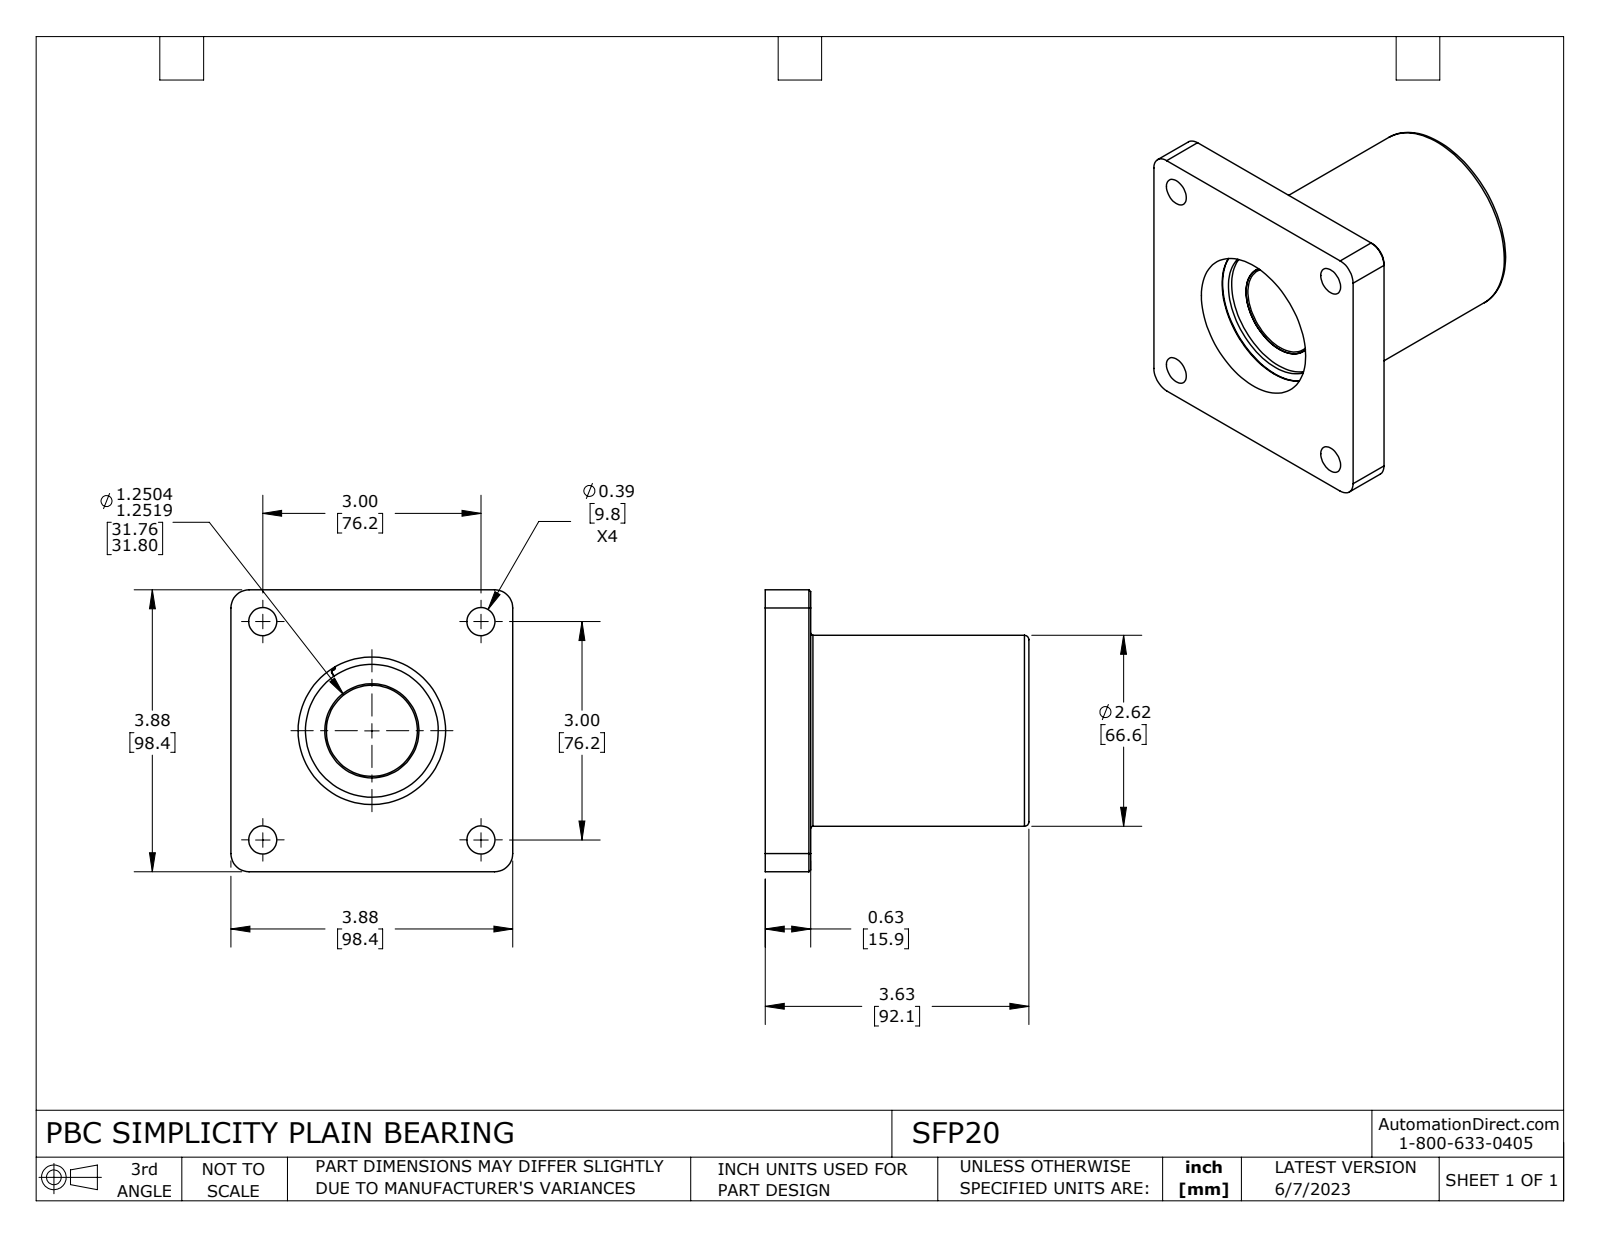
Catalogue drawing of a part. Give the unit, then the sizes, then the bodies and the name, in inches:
Units: inches
Overall size (bounding box): 3.875 × 3.875 × 3.625
Round holes (diameter × count): ⌀0.386 ×4, ⌀1.252 ×1, ⌀1.295 ×1, ⌀1.826 ×1, ⌀2.028 ×1, ⌀2.122 ×1
Round bosses / shafts (diameter × count): ⌀2.624 ×1, ⌀2.142 ×1, ⌀1.999 ×1, ⌀1.889 ×1, ⌀1.838 ×1
Partial cylindrical surfaces — rounded edges, fillets, slot ends (radius × count): R0.026 ×4, R0.25 ×4, R0.021 ×2, R0.031 ×2
Main face-to-face distances: 0.625, 3.875, 0.488, 3.137, 0.503, 3.121, 0.122, 2.618, 2.496, 3.625
Hole centre spacings: 2.121, 3, 4.243
Volume: 18.61 in³ · Surface area: 147.2 in²
Bodies: 7 solids, 169 faces (41 planar, 74 cylindrical, 54 other)
Part name (STEP PRODUCT): SFP20
STEP written by: SolidWorks 2021 (CONFIG_CONTROL_DESIGN)
